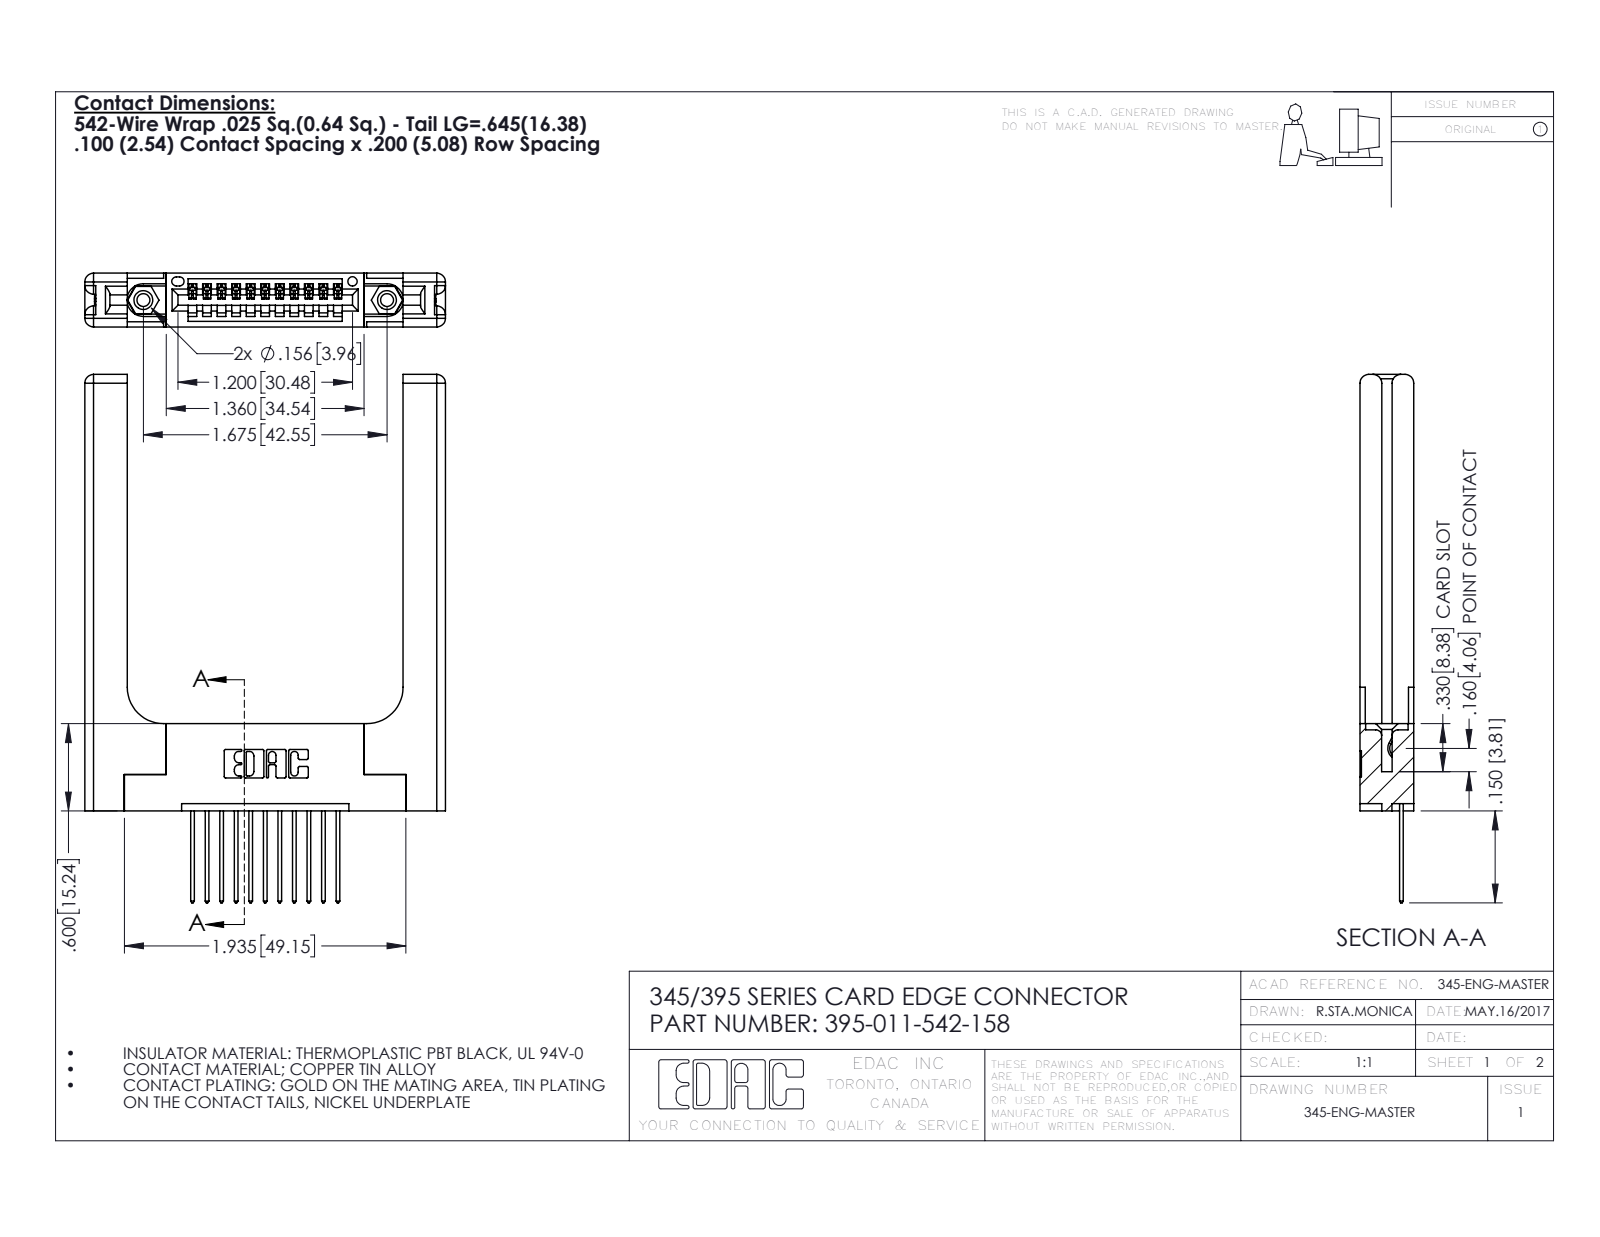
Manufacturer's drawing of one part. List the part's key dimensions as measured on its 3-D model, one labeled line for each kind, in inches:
Part name (STEP PRODUCT): 345-220-058_345-220-058; 345-292-001_345-293-142; 395-011-542-158; 345-250-001_345-250-001-102 (+1 more)
STEP written by: SolidWorks 2016 (CONFIG_CONTROL_DESIGN)
Units: inches
Bodies: 16 solids, 1020 faces (668 planar, 292 cylindrical, 60 other)
Overall size (bounding box): 3.632 × 2.479 × 0.37
Volume: 0.87 in³ · Surface area: 19.66 in²
Round holes (diameter × count): ⌀0.089 ×2, ⌀0.125 ×2, ⌀0.156 ×2, ⌀0.064 ×1
Round bosses / shafts (diameter × count): ⌀0.155 ×2
Partial cylindrical surfaces — rounded edges, fillets, slot ends (radius × count): R0.006 ×22, R0.01 ×22, R0.01 ×22, R0.06 ×16, R0.007 ×6, R0.031 ×6, R0.026 ×3, R0.03 ×2
Main face-to-face distances: 0.37, 0.072, 0.15, 0.298, 0.22, 0.077, 0.148, 0.2, 1.896, 0.098
Hole centre spacings: 0.27, 1.443, 1.675
